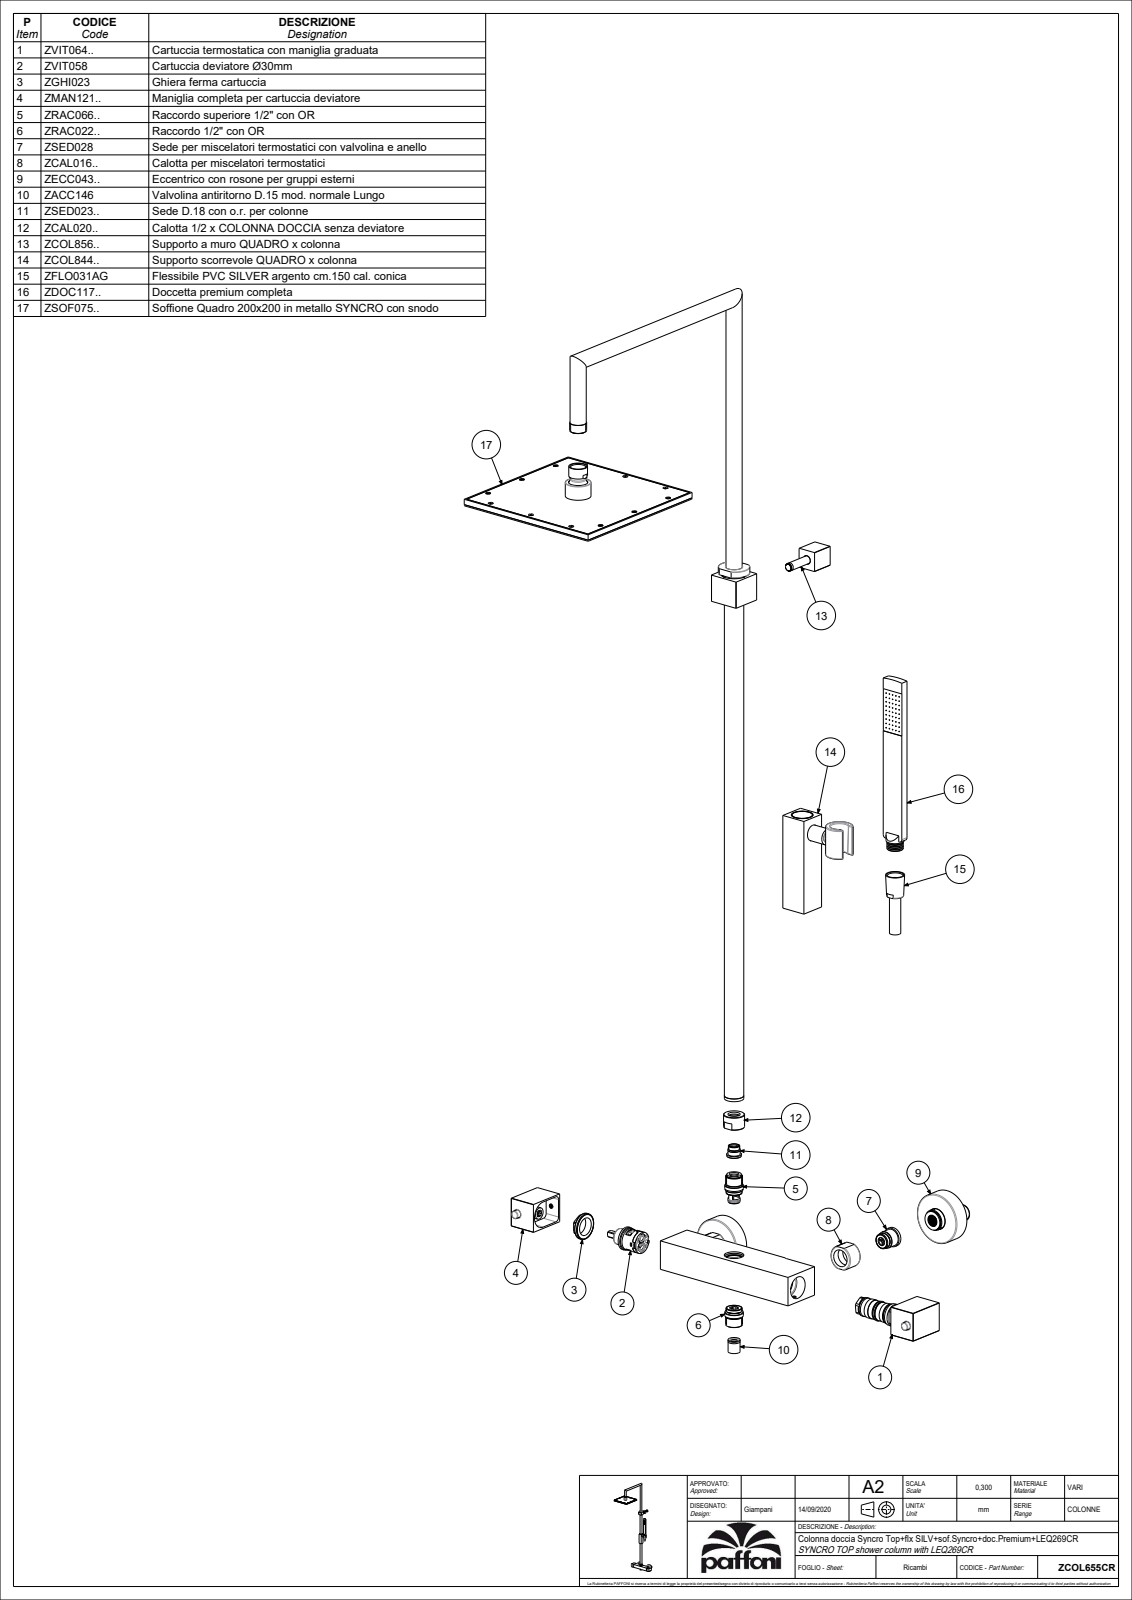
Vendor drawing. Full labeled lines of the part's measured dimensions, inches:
Part name (STEP PRODUCT): ZCOL655CR
STEP written by: CREO PARAMETRIC BY PTC INC, 2020044 (CONFIG_CONTROL_DESIGN)
Units: inches
Bodies: 8 solids, 1892 faces (552 planar, 430 cylindrical, 910 other)
Overall size (bounding box): 44.803 × 18.732 × 10.986
Volume: 89.77 in³ · Surface area: 652.3 in²
Round holes (diameter × count): ⌀0.236 ×4, ⌀0.098 ×2, ⌀0.118 ×2, ⌀0.128 ×2, ⌀0.157 ×2, ⌀0.177 ×2, ⌀0.217 ×2, ⌀0.252 ×2, ⌀0.398 ×2, ⌀0.689 ×2, ⌀0.795 ×2, ⌀0.85 ×2
Round bosses / shafts (diameter × count): ⌀0.236 ×12, ⌀0.787 ×4, ⌀2.5 ×2, ⌀0.571 ×2, ⌀0.512 ×2, ⌀0.386 ×2, ⌀0.299 ×2, ⌀1.252 ×1
Partial cylindrical surfaces — rounded edges, fillets, slot ends (radius × count): R0.039 ×94, R0.02 ×16, R0.197 ×6, R0.069 ×2, R0.157 ×2, R0.19 ×2, R0.614 ×2, R0.089 ×1
Main face-to-face distances: 0.335, 1.476, 0.118, 1.368, 0.108, 0.531, 1.457, 38.72, 39.055, 37.244
Hole centre spacings: 0.236, 0.394, 0.602, 0.609, 16.525, 0.157, 0.238, 0.246
